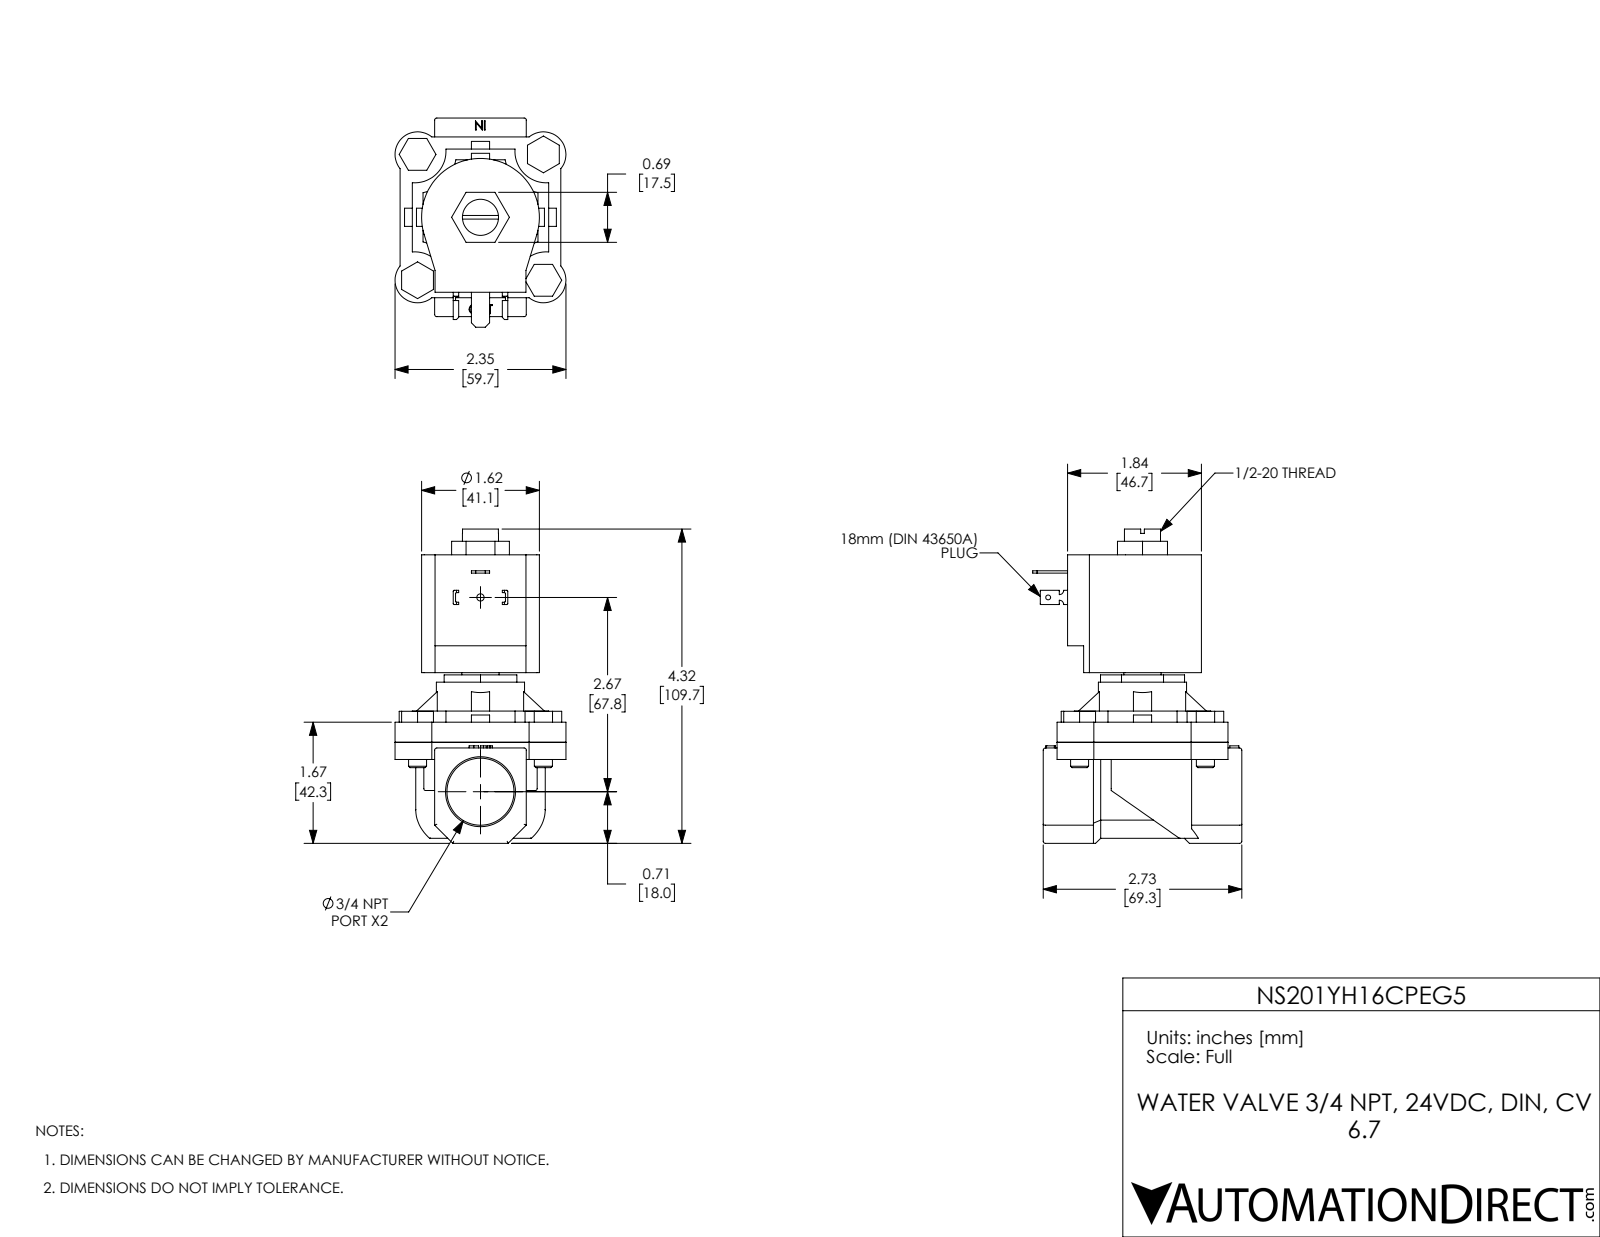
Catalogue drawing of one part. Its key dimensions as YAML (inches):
part_name: "NS201YH16CPEG5"
step_written_by: "SolidWorks 2024 (CONFIG_CONTROL_DESIGN)"
units: inches
bodies: {solids: 11, faces: 387, planar: 241, cylindrical: 113, other: 33}
overall_size: [4.32, 2.875, 2.35]
volume: 10.62
surface_area: 70.92
round_holes:
  - {diameter: 0.25, count: 4}
  - {diameter: 0.067, count: 1}
  - {diameter: 0.1, count: 1}
  - {diameter: 0.496, count: 1}
  - {diameter: 0.512, count: 1}
  - {diameter: 0.922, count: 1}
  - {diameter: 1.155, count: 1}
round_bosses_or_shafts:
  - {diameter: 0.248, count: 4}
  - {diameter: 1.213, count: 1}
partial_cylinders:
  - {radius: 0.03, count: 15}
  - {radius: 0.015, count: 8}
  - {radius: 0.31, count: 4}
  - {radius: 0.432, count: 4}
  - {radius: 0.579, count: 4}
  - {radius: 0.06, count: 2}
  - {radius: 0.81, count: 1}
  - {radius: 0.89, count: 1}
face_to_face_distances: [0.276, 2.577, 2.301, 0.236, 0.512, 2.813, 0.475, 1.735, 1.26, 2.21]
hole_center_spacings: [1.223, 1.73, 2.446, 2.67]
